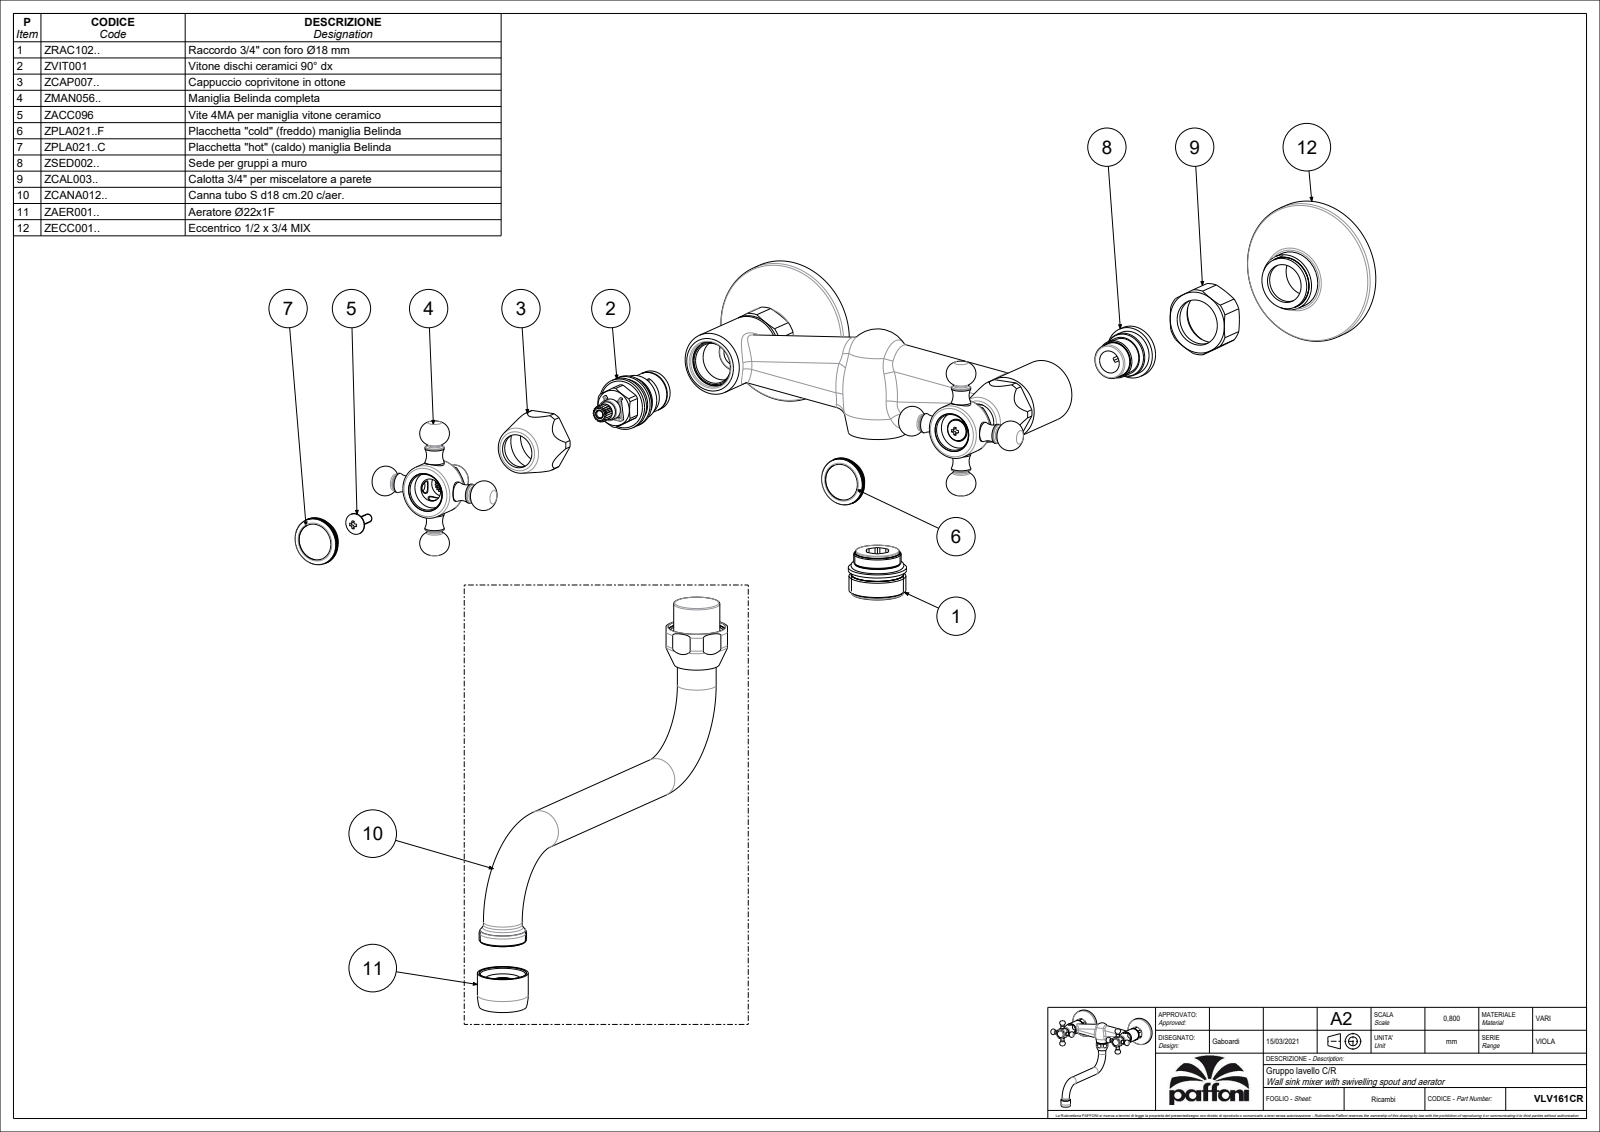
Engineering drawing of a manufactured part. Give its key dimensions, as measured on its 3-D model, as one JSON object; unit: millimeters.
{"part_name": "VLV161CR", "step_written_by": "CREO PARAMETRIC BY PTC INC, 2020044 (CONFIG_CONTROL_DESIGN)", "units": "millimeters", "bodies": {"solids": 3, "faces": 1497, "planar": 645, "cylindrical": 448, "other": 404}, "overall_size": [245.8, 223.5, 180.95], "volume_mm3": 291883, "surface_area_mm2": 96593, "round_holes": [[10.5, 2], [15.7, 2], [19, 2], [21.3, 2], [23, 2], [12.6, 1], [13.8, 1], [16.1, 1], [16.6, 1], [18.2, 1], [18.7, 1], [21, 1]], "round_bosses_or_shafts": [[18, 3], [14, 3], [9, 3], [7, 3], [65.5, 2], [29, 2], [25, 2], [22, 2]], "partial_cylinders_radius": [[6.5, 4], [10, 4], [3.5, 2], [15.5, 2], [5.25, 1], [15, 1]], "face_to_face_distances": [16.5, 3.5, 28.5, 26.5, 8.5, 10, 12, 1.5, 20, 34], "hole_center_spacings": [158]}
